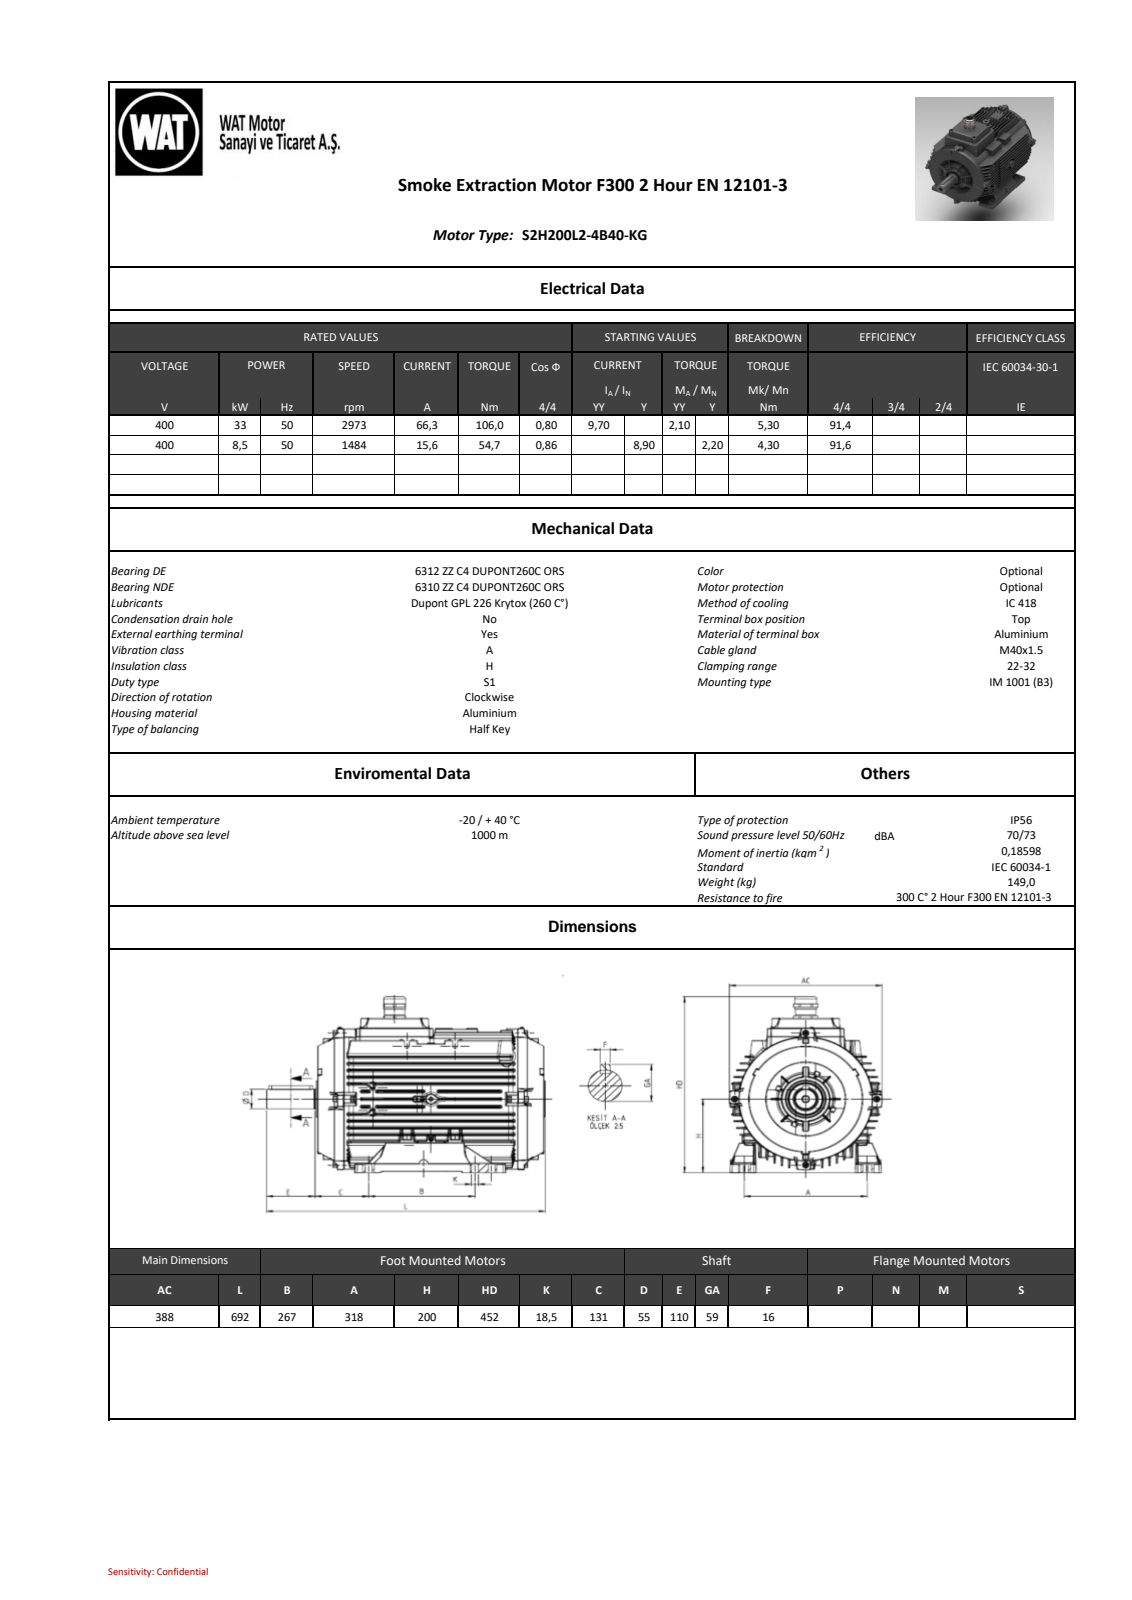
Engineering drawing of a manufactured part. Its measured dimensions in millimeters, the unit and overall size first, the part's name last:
Units: millimetres
Overall size (bounding box): 692 × 452 × 388.08
Round holes (diameter × count): ⌀5.6 ×4, ⌀21 ×1, ⌀32 ×1, ⌀62 ×1, ⌀80 ×1, ⌀85.8 ×1, ⌀86 ×1, ⌀90 ×1
Round bosses / shafts (diameter × count): ⌀12.73 ×8, ⌀8 ×8, ⌀10 ×4, ⌀14.8 ×3, ⌀303 ×1, ⌀296 ×1, ⌀60.2 ×1, ⌀55.3 ×1
Partial cylindrical surfaces — rounded edges, fillets, slot ends (radius × count): R1 ×612, R2 ×517, R0.5 ×59, R4 ×41, R5 ×39, R3 ×16, R1.5 ×15, R8 ×10
Main face-to-face distances: 16.21, 32.48, 16.27, 171.05, 154.78, 138.57, 157.62, 16.31, 32.58, 48.79
Bodies: 0 solids, 6845 faces (1398 planar, 2060 cylindrical, 3387 other)
Part name (STEP PRODUCT): AD_objects
STEP written by: SIEMENS PLM Software NX2206.8101 (AP203_CONFIGURATION_CONTROLLED_3D_DESIGN_OF_MECHANICAL_PARTS_AND_ASSEMBLIES_MIM_LF)
